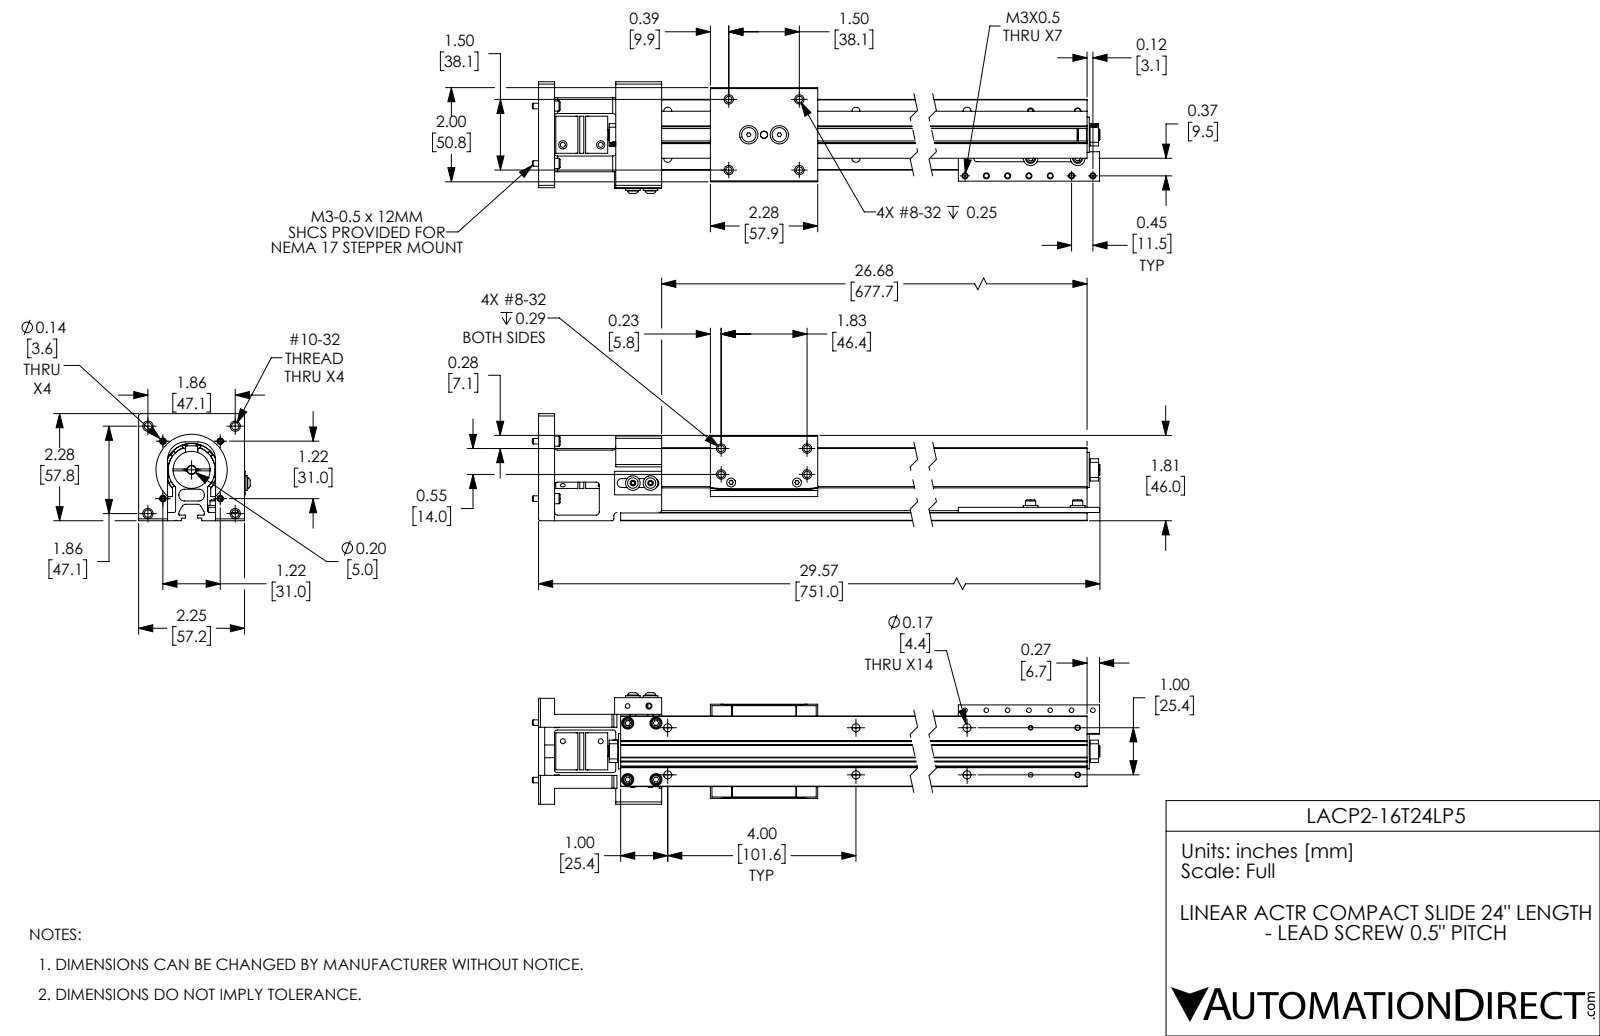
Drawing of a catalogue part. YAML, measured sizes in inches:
part_name: "LACP2-16T24LP5; LACP2-16T24LP5_BLOCK; LACP2-16T24LP5_BODY"
step_written_by: "SolidWorks 2017 (AUTOMOTIVE_DESIGN)"
units: inches
bodies: {solids: 47, faces: 1257, planar: 504, cylindrical: 483, other: 270}
overall_size: [29.7, 2.37, 2.275]
volume: 28.33
surface_area: 429.4
round_holes:
  - {diameter: 0.098, count: 18}
  - {diameter: 0.172, count: 14}
  - {diameter: 0.136, count: 10}
  - {diameter: 0.141, count: 4}
  - {diameter: 0.147, count: 4}
  - {diameter: 0.159, count: 4}
  - {diameter: 0.257, count: 4}
  - {diameter: 0.099, count: 2}
  - {diameter: 0.106, count: 2}
  - {diameter: 0.118, count: 2}
  - {diameter: 0.125, count: 2}
  - {diameter: 0.125, count: 2}
round_bosses_or_shafts:
  - {diameter: 0.217, count: 10}
  - {diameter: 0.118, count: 10}
  - {diameter: 0.312, count: 4}
  - {diameter: 0.118, count: 4}
  - {diameter: 0.307, count: 2}
  - {diameter: 0.224, count: 2}
  - {diameter: 0.164, count: 2}
  - {diameter: 0.138, count: 2}
partial_cylinders:
  - {radius: 0.01, count: 17}
  - {radius: 0.05, count: 9}
  - {radius: 0.039, count: 8}
  - {radius: 0.065, count: 7}
  - {radius: 0.02, count: 4}
  - {radius: 0.074, count: 4}
  - {radius: 0.079, count: 4}
  - {radius: 0.118, count: 4}
face_to_face_distances: [0.175, 0.679, 0.175, 0.411, 1.089, 0.419, 0.67, 0.244, 0.495, 0.251]
hole_center_spacings: [1, 4, 4.123, 8, 8.062, 1.2, 0.863, 1.312]
